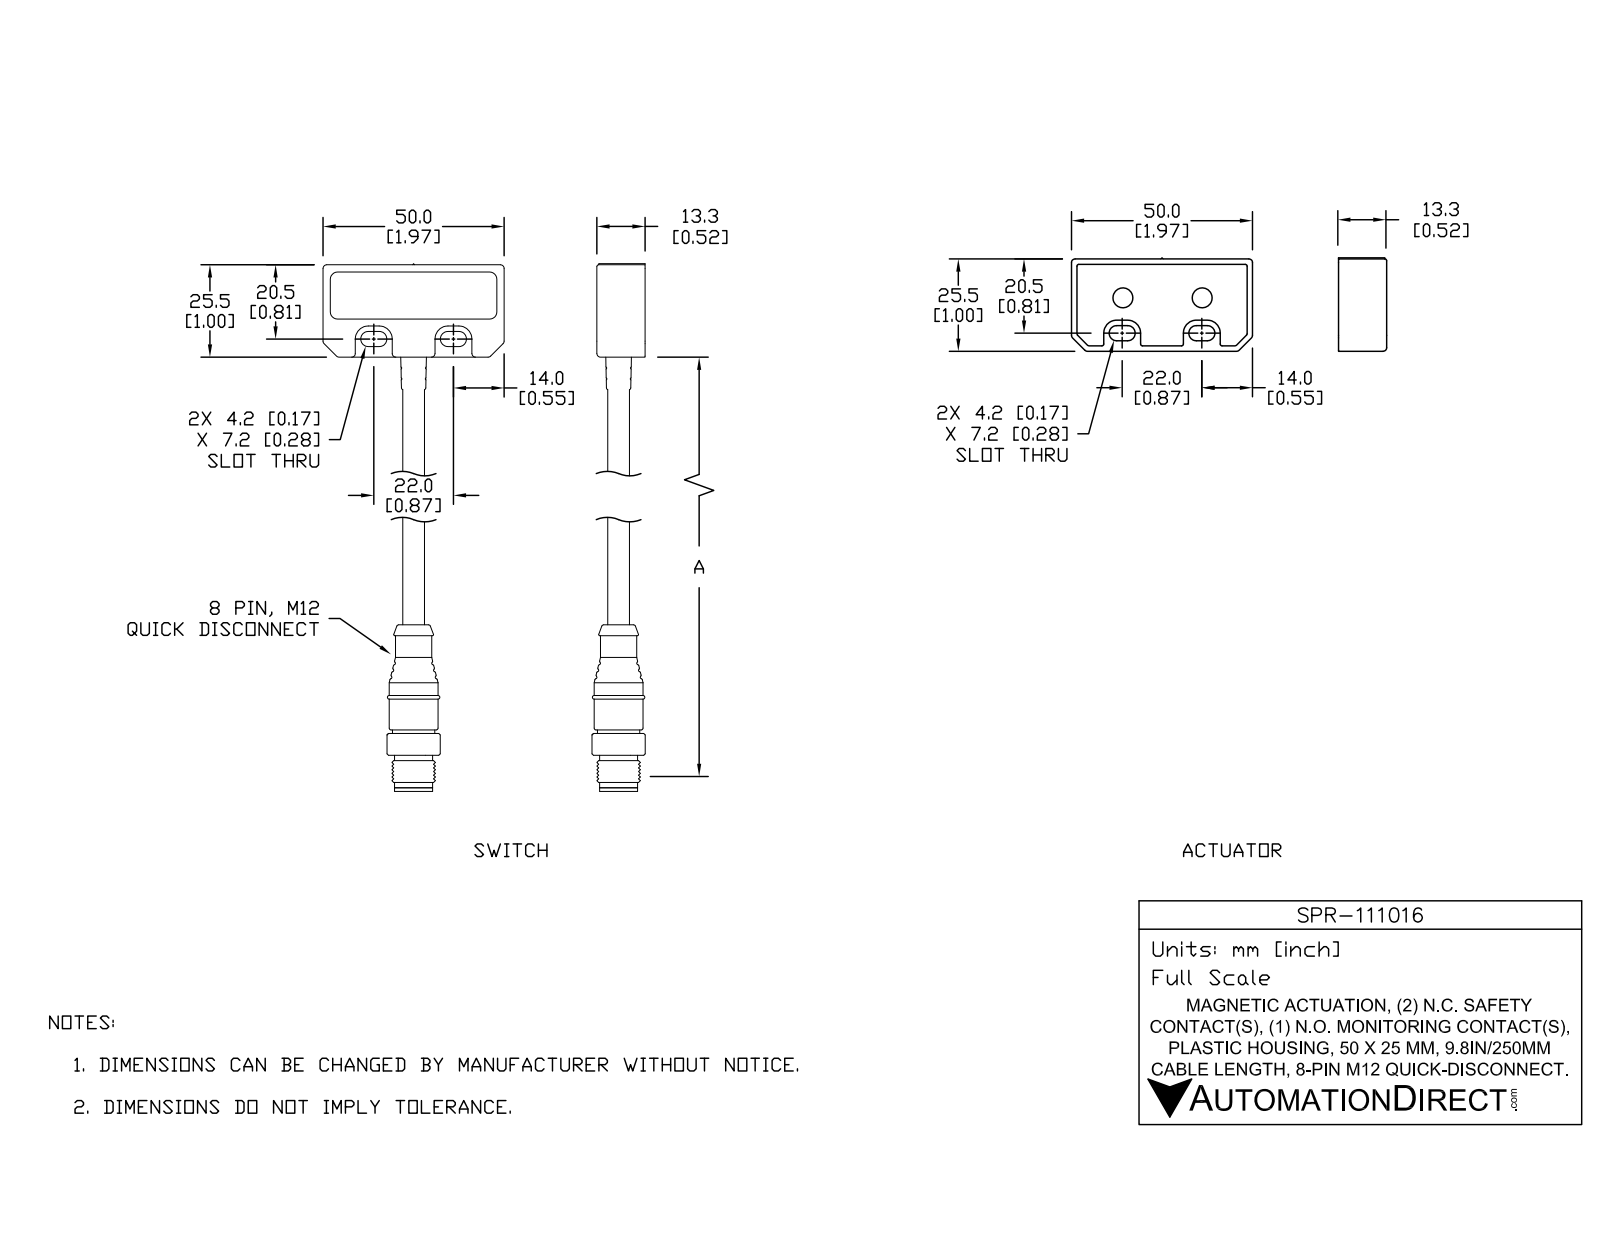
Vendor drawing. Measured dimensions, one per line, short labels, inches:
name: SPR-111016_2; SPR-111016_1; SPR-111016
written by: SolidWorks 2017 (AUTOMOTIVE_DESIGN)
unit: in
bodies: 4 solids, 191 faces (61 planar, 80 cylindrical, 50 other)
size: 5.885 × 1.969 × 0.524
volume: 2.063 in³; area: 18.22 in²
bosses: 1× ⌀0.236
rounds: 36× R0.039, 8× R0.079, 8× R0.083, 8× R0.142, 2× R0.02
face distances: 0.512, 1.004, 1.043, 0.524, 0.039, 1.969, 2.047, 0.165, 0.177, 0.346
